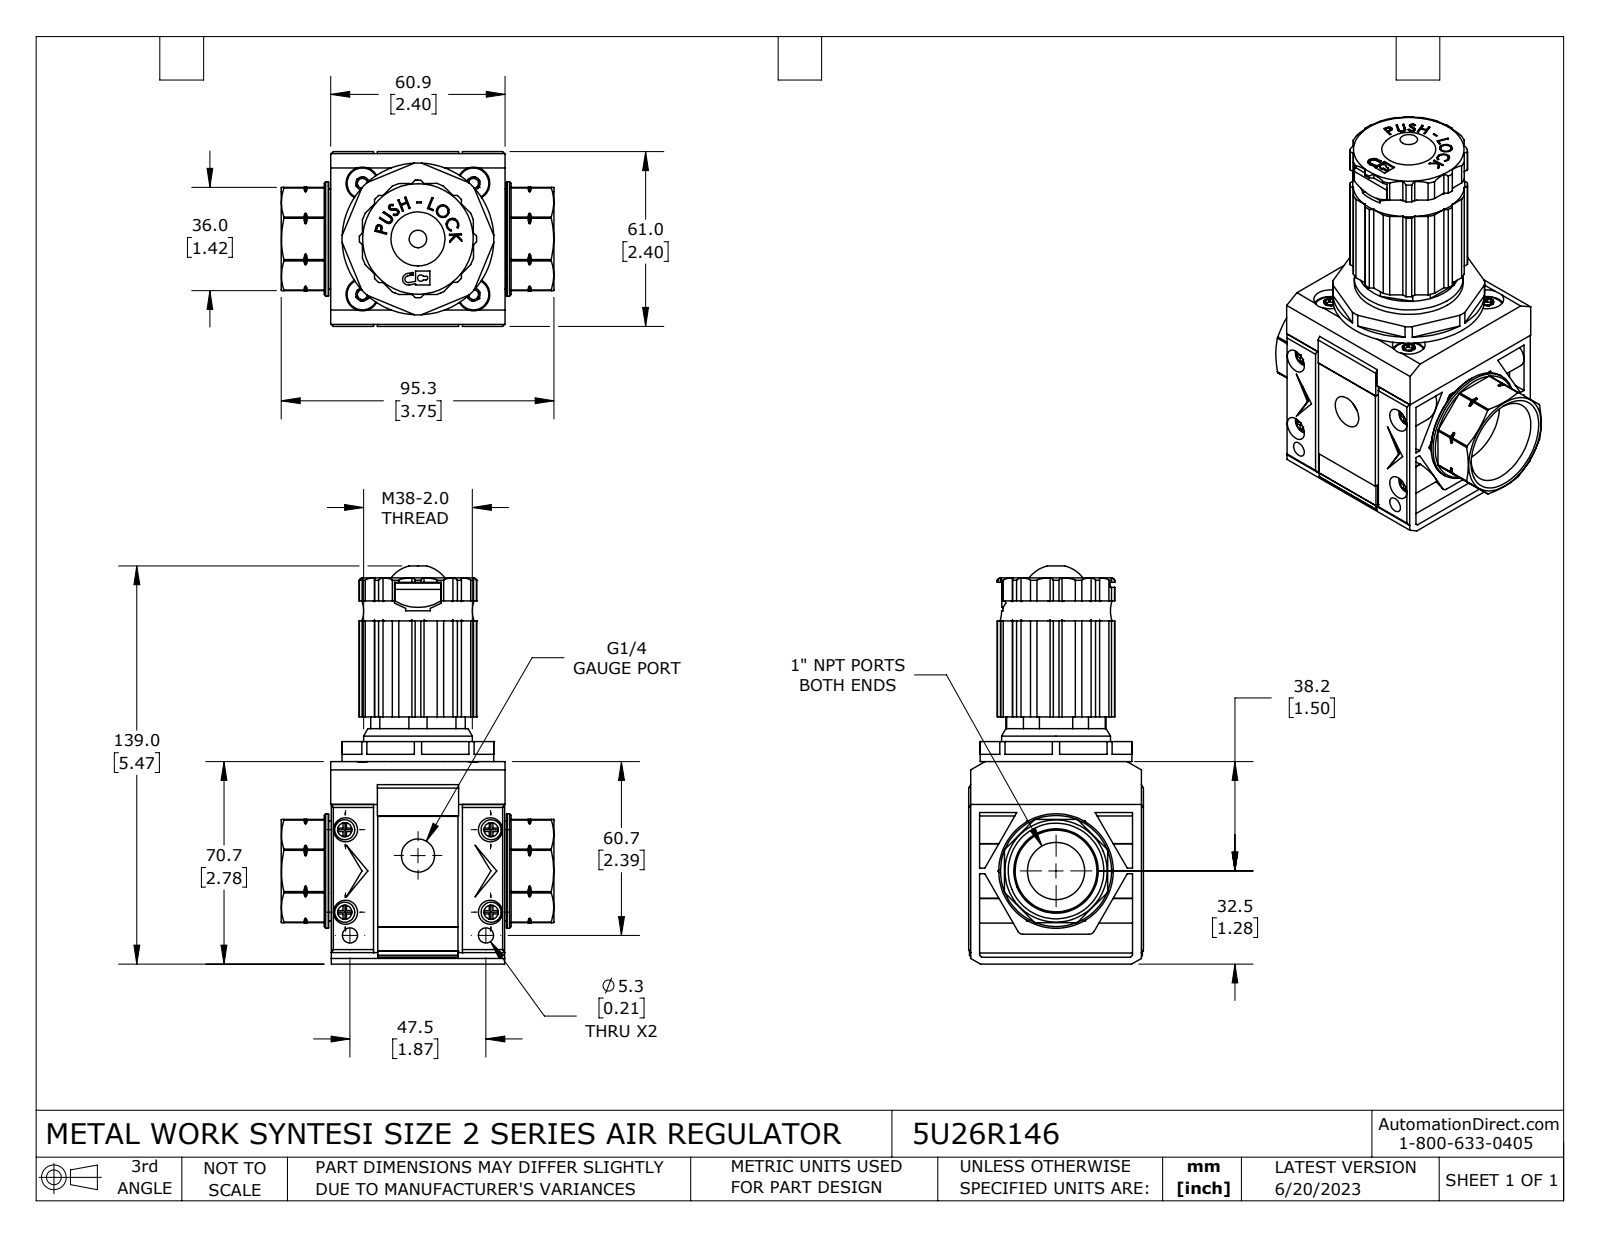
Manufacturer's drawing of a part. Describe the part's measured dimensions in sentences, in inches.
The part is named "5U26R146". Its 3-D file was written by "SolidWorks 2021 (CONFIG_CONTROL_DESIGN)". It is 13 solids with 1241 faces: 630 planar, 395 cylindrical and 216 other. Overall it measures 5.472 by 3.75 by 2.402 inches. Its volume is 17.64 cubic inches and its surface area 139.9 square inches. Round holes: 4 of diameter 0.128, 4 of diameter 0.165, 4 of diameter 0.331, 4 of diameter 0.449, 2 of diameter 0.209, 1 of diameter 0.457, 1 of diameter 0.787, 1 of diameter 1.25, 1 of diameter 1.411, 1 of diameter 1.508. Round bosses or shafts: 4 of diameter 0.276, 4 of diameter 0.189, 4 of diameter 0.15, 1 of diameter 2.087, 1 of diameter 1.575, 1 of diameter 1.496, 1 of diameter 1.378, 1 of diameter 1.248. Partial cylindrical surfaces (rounded edges, fillets, slot ends): 28 of radius 0.011, 4 of radius 0.069, 4 of radius 0.191, 4 of radius 0.807, 2 of radius 0.079, 2 of radius 0.242, 1 of radius 0.022, 1 of radius 0.025. The main face-to-face distances are 2.39, 0.094, 2.193, 2.098, 0.591, 2.783, 2.689, 0.028, 2.402, 0.299. The hole center spacings are 1.08, 1.528, 0.325, 1.057, 1.134, 1.265, 1.443, 1.454.
